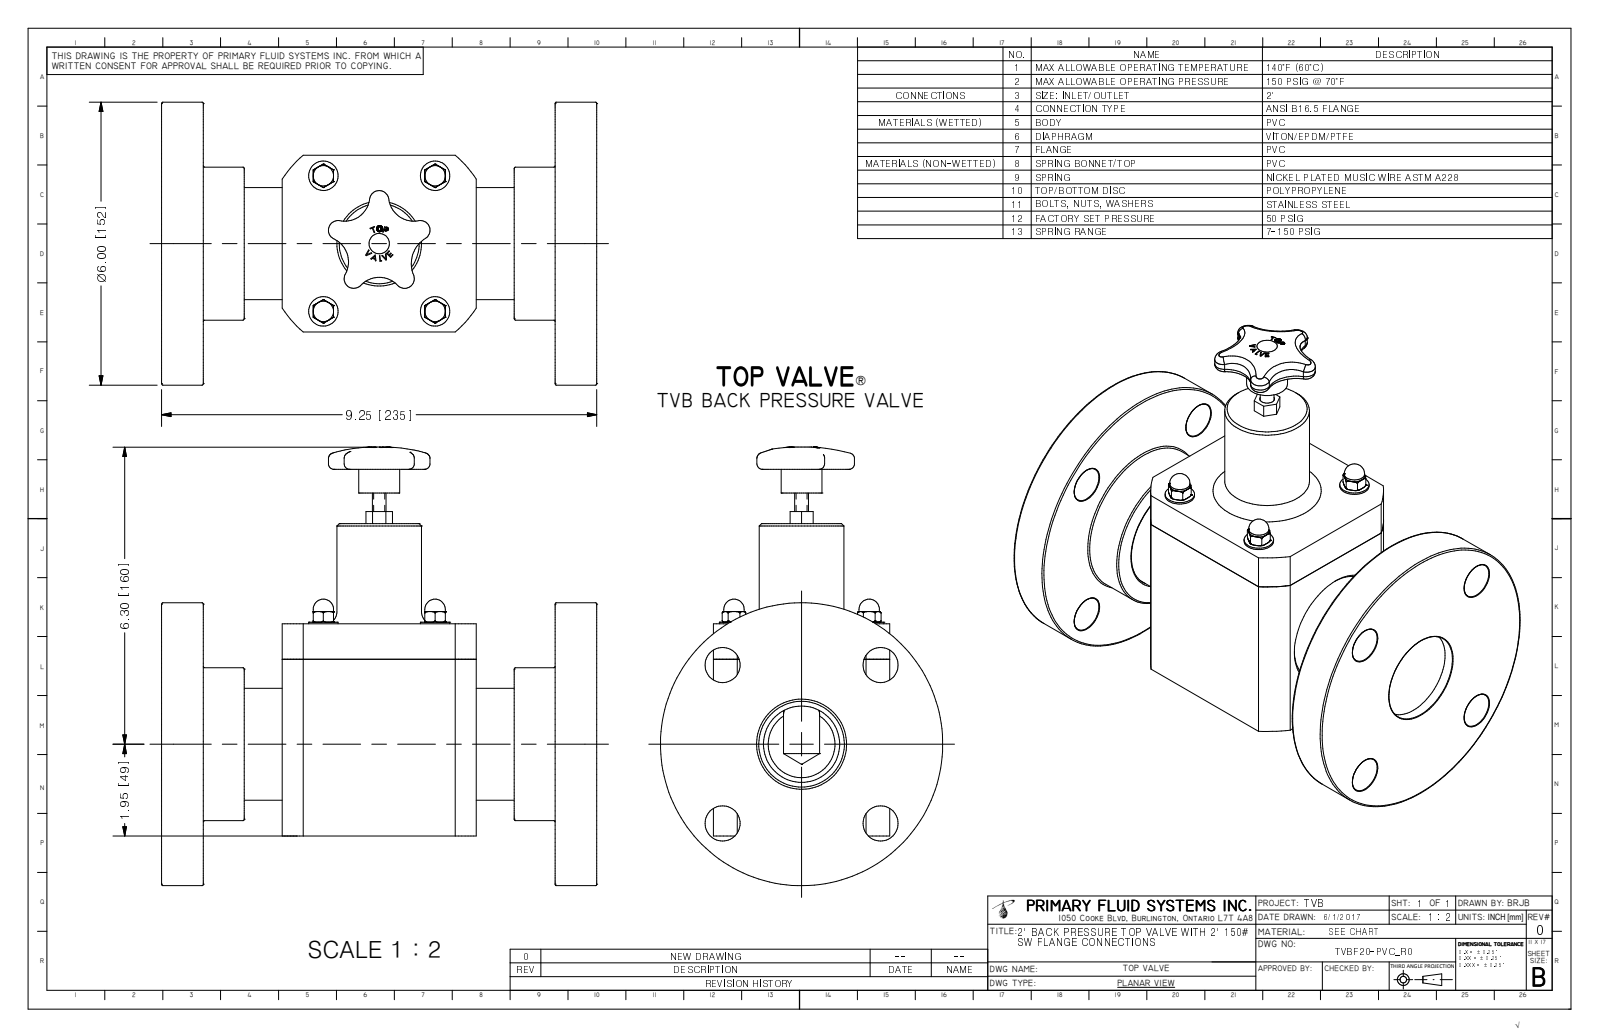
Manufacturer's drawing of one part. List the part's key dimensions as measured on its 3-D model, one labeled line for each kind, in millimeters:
Part name (STEP PRODUCT): TVBF20-PVC_R0
STEP written by: Autodesk Inventor 2009 (AUTOMOTIVE_DESIGN)
Units: millimetres
Bodies: 1 solid, 393 faces (152 planar, 61 cylindrical, 180 other)
Overall size (bounding box): 217.8 × 205.2 × 127
Volume: 1 454 000 mm³ · Surface area: 181 000 mm²
Round holes (diameter × count): ⌀4.4 ×4, ⌀16 ×4, ⌀37.5 ×1, ⌀38.1 ×1
Round bosses / shafts (diameter × count): ⌀15.9 ×4, ⌀11 ×4, ⌀9.5 ×4, ⌀127 ×1, ⌀66.5 ×1, ⌀48.3 ×1, ⌀45.7 ×1, ⌀22.1 ×1
Partial cylindrical surfaces — rounded edges, fillets, slot ends (radius × count): R2.2 ×5, R5.2 ×5, R13.6 ×4, R16.7 ×4, R15.9 ×1, R18.9 ×1, R60.3 ×1
Main face-to-face distances: 19.8, 185.4, 205.2, 82.6, 50.2, 155, 30.4, 135.2, 165.6, 101.6
Hole centre spacings: 49.2, 69.6, 60.3, 60.3, 85.3, 98.4
